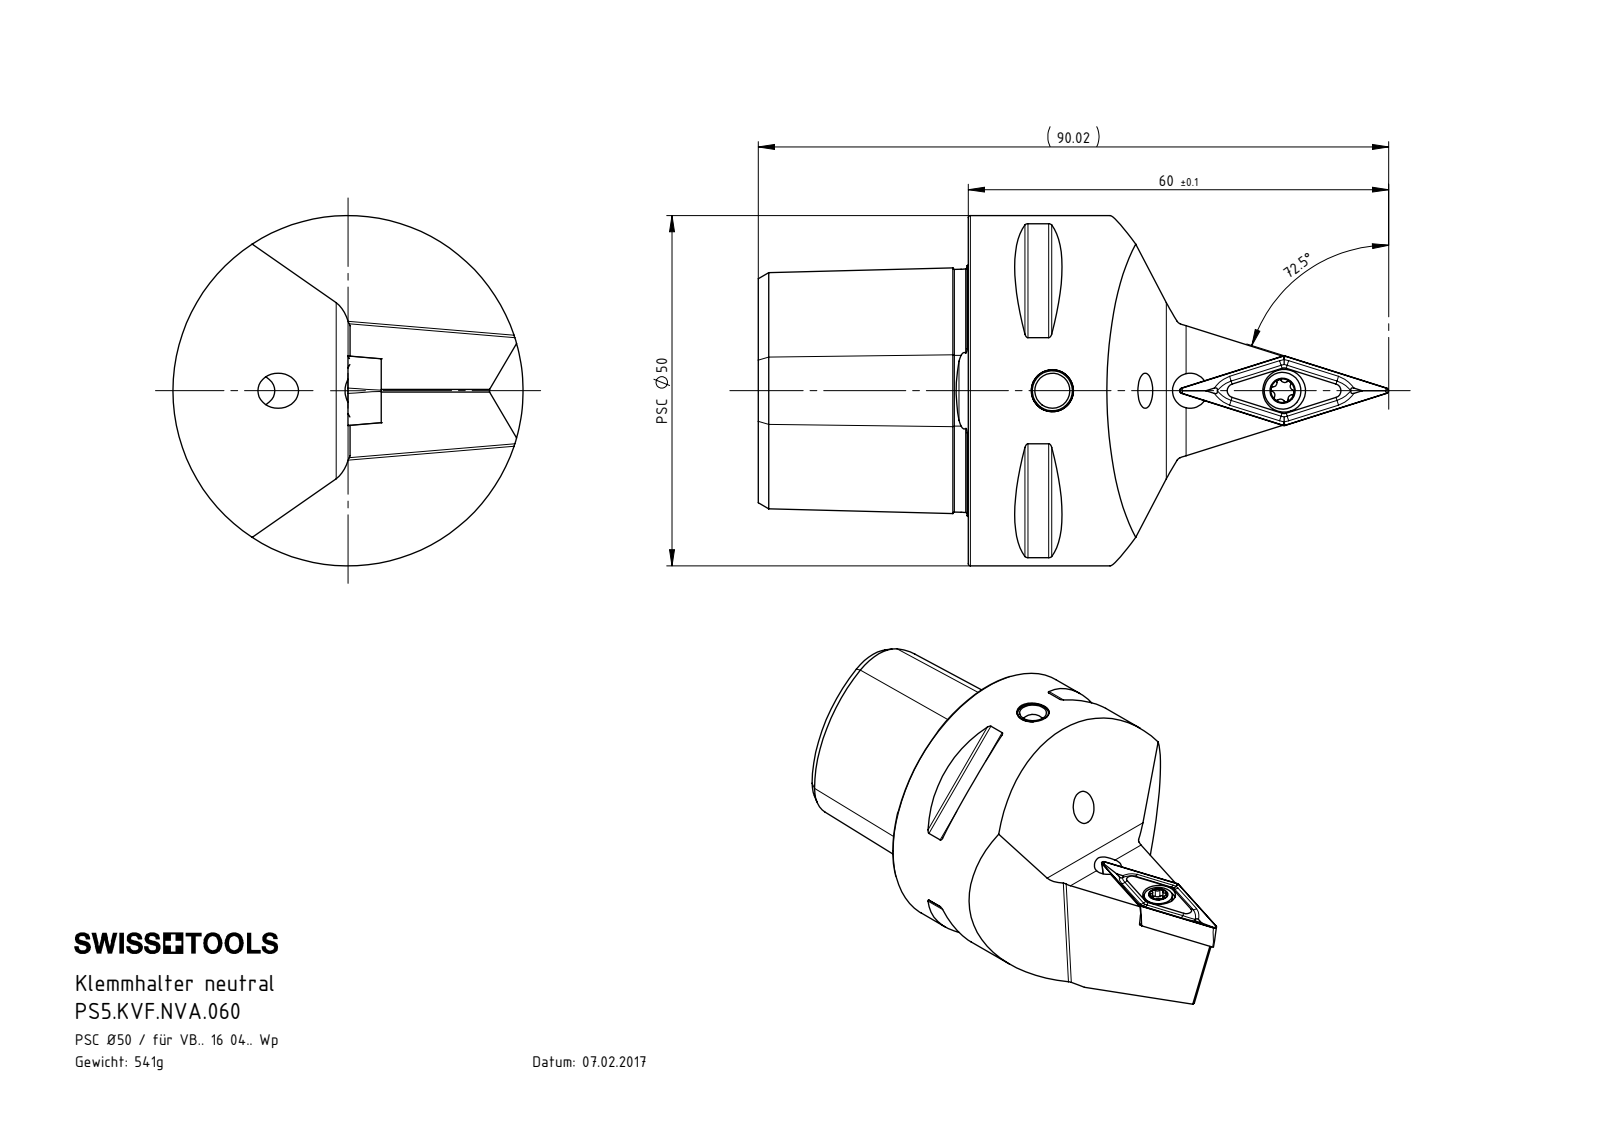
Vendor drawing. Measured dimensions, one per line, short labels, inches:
name: WCB-ER2.001.009_A; VBMT160404; PS5.KVF.NVA.060; KVT_MB_600_060 (+1 more)
written by: SolidWorks 2017 (AUTOMOTIVE_DESIGN)
unit: in
bodies: 6 solids, 206 faces (61 planar, 47 cylindrical, 98 other)
size: 3.543 × 1.969 × 1.969
volume: 4.221 in³; area: 27.34 in²
holes: 3× ⌀0.197, 2× ⌀0.24, 1× ⌀0.13, 1× ⌀0.157, 1× ⌀0.173, 1× ⌀0.571, 1× ⌀0.827, 1× ⌀0.945
bosses: 1× ⌀1.969, 1× ⌀0.236, 1× ⌀0.207, 1× ⌀0.157
rounds: 8× R0.02, 6× R0.013, 6× R0.023, 2× R0.006, 2× R0.031, 1× R0.118, 1× R0.157
face distances: 1.181, 0.176, 0.755, 1.748, 0.787, 0.394, 0.354, 1.173, 0.386, 0.187
hole spacings: 0.52, 0.529, 0.774, 1.024, 1.294, 1.303, 1.797, 2.318
